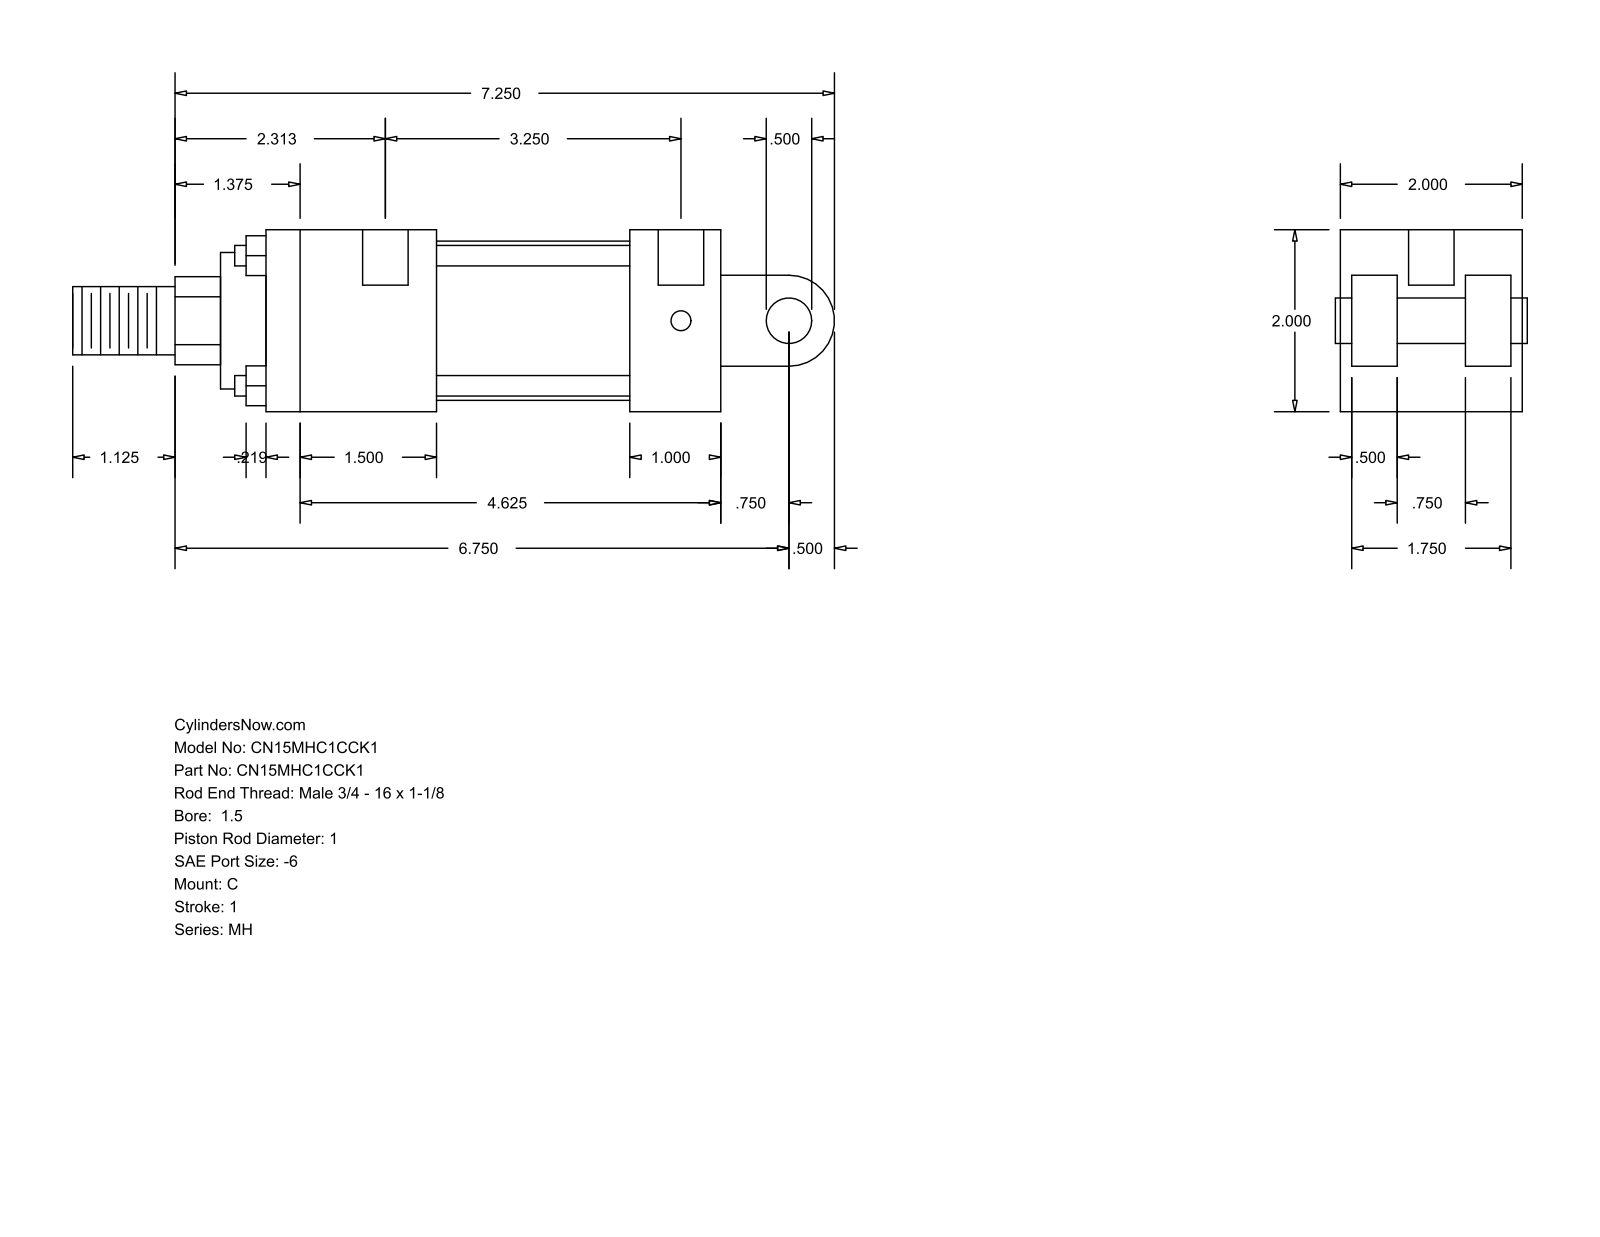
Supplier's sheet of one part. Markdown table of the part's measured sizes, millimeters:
| quantity | value |
| --- | --- |
| part name | MH_C__0150_1 |
| STEP written by | GSSL Pune (CONFIG_CONTROL_DESIGN) |
| units | millimeters |
| bodies | 0 solids, 99 faces (70 planar, 29 cylindrical, 0 other) |
| overall size | 212.72 × 50.8 × 50.8 |
| round holes (diameter × count) | 5.56 × 4, 12.7 × 2 |
| round bosses / shafts (diameter × count) | 5.71 × 4, 44.45 × 1, 38.1 × 1, 25.4 × 1, 19.05 × 1, 12.7 × 1 |
| partial cylindrical surfaces (radius × count) | 12.29 × 1, 12.7 × 1 |
| main face-to-face distances | 50.8, 12.7, 47.63, 25.4, 3.17, 15.87, 34.93, 31.76, 53.97, 101.6 |
| hole center spacings | 85.73, 3.18, 82.55 |
